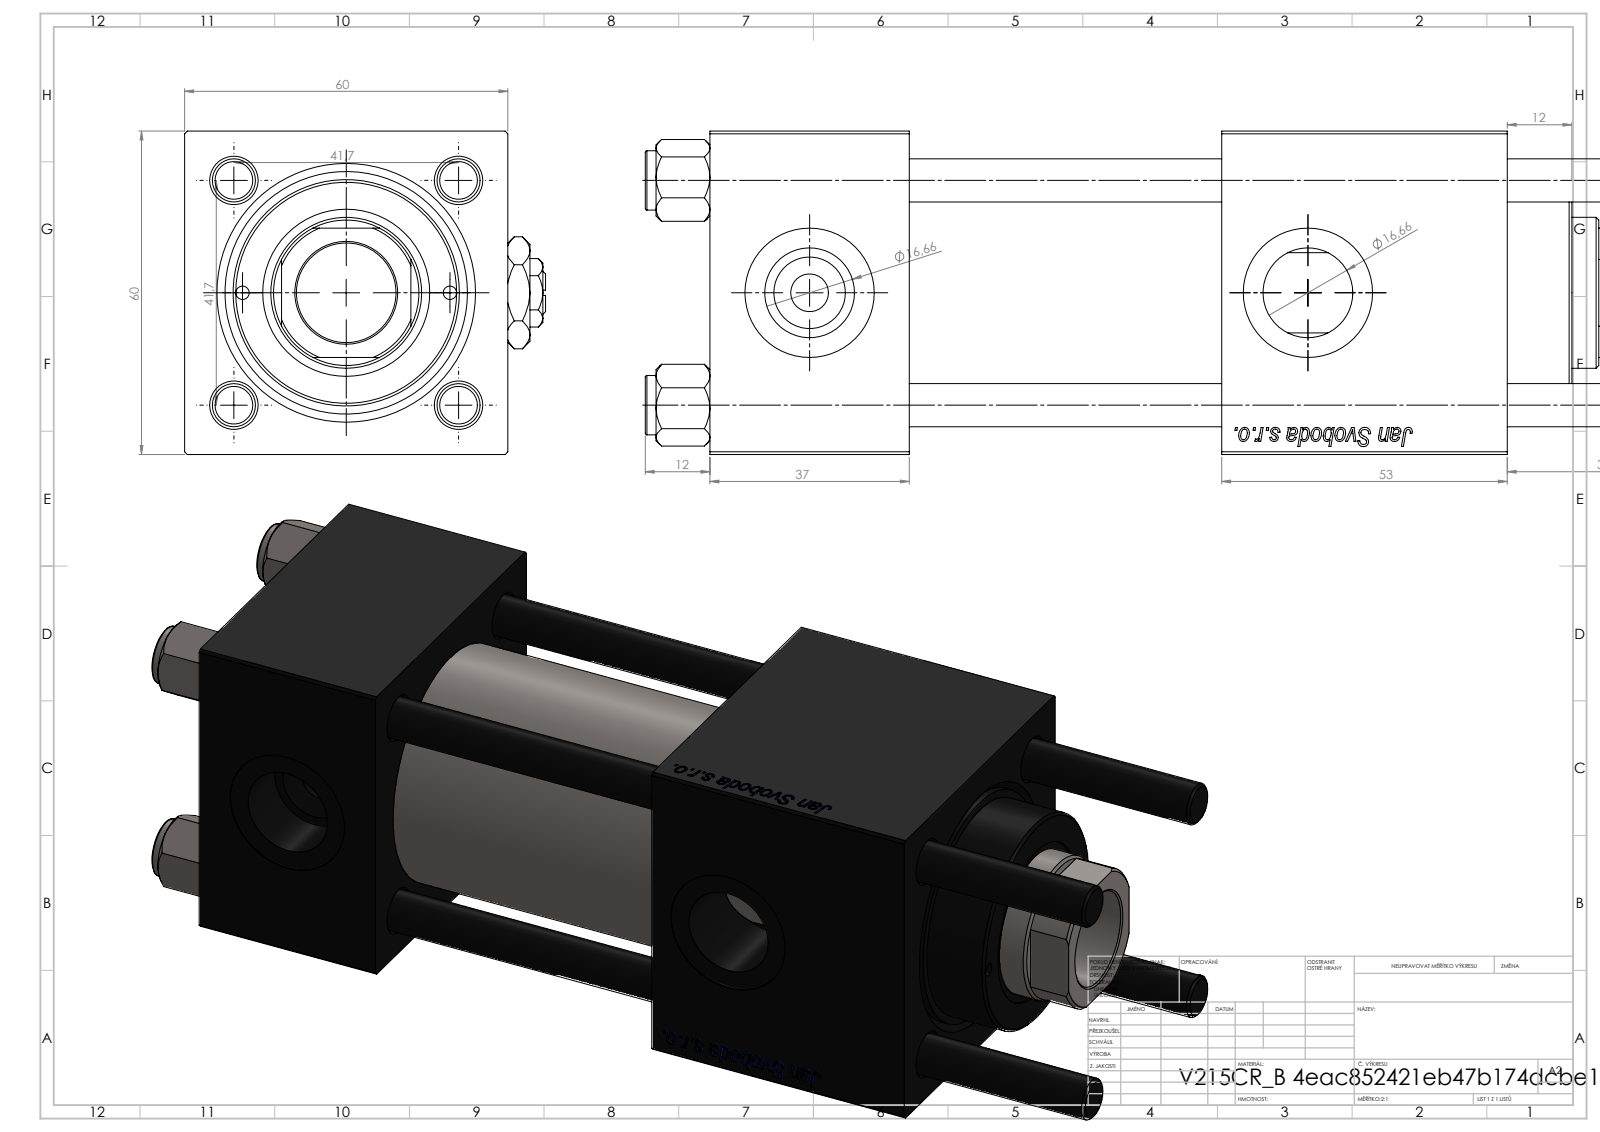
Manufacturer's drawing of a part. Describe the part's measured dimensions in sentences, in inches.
The part is named "V215CR_VCP_B; V215_VC_A; V215CR_B-1; NUT_M5_B (+2 more)". Its 3-D file was written by "SolidWorks 2019 (CONFIG_CONTROL_DESIGN)". It is 13 solids with 1265 faces: 483 planar, 92 cylindrical and 690 other. Overall it measures 7.677 by 2.638 by 2.362 inches. Its volume is 26.37 cubic inches and its surface area 190.7 square inches. Round holes: 4 of diameter 0.315, 2 of diameter 0.098, 2 of diameter 0.276, 2 of diameter 0.656, 2 of diameter 0.945, 1 of diameter 0.728, 1 of diameter 1.102, 1 of diameter 1.22, 1 of diameter 1.575, 1 of diameter 1.772. Round bosses or shafts: 4 of diameter 0.433, 1 of diameter 1.811, 1 of diameter 1.654. Partial cylindrical surfaces (rounded edges, fillets, slot ends): 1 of radius 0.531. The main face-to-face distances are 2.362, 1.457, 2.283, 3.74, 2.087, 4.697, 3.24, 0.957, 5.827, 4.37. The hole center spacings are 0.823, 1.161, 1.642, 1.78, 0.758, 2.322, 1.516, 3.642.
